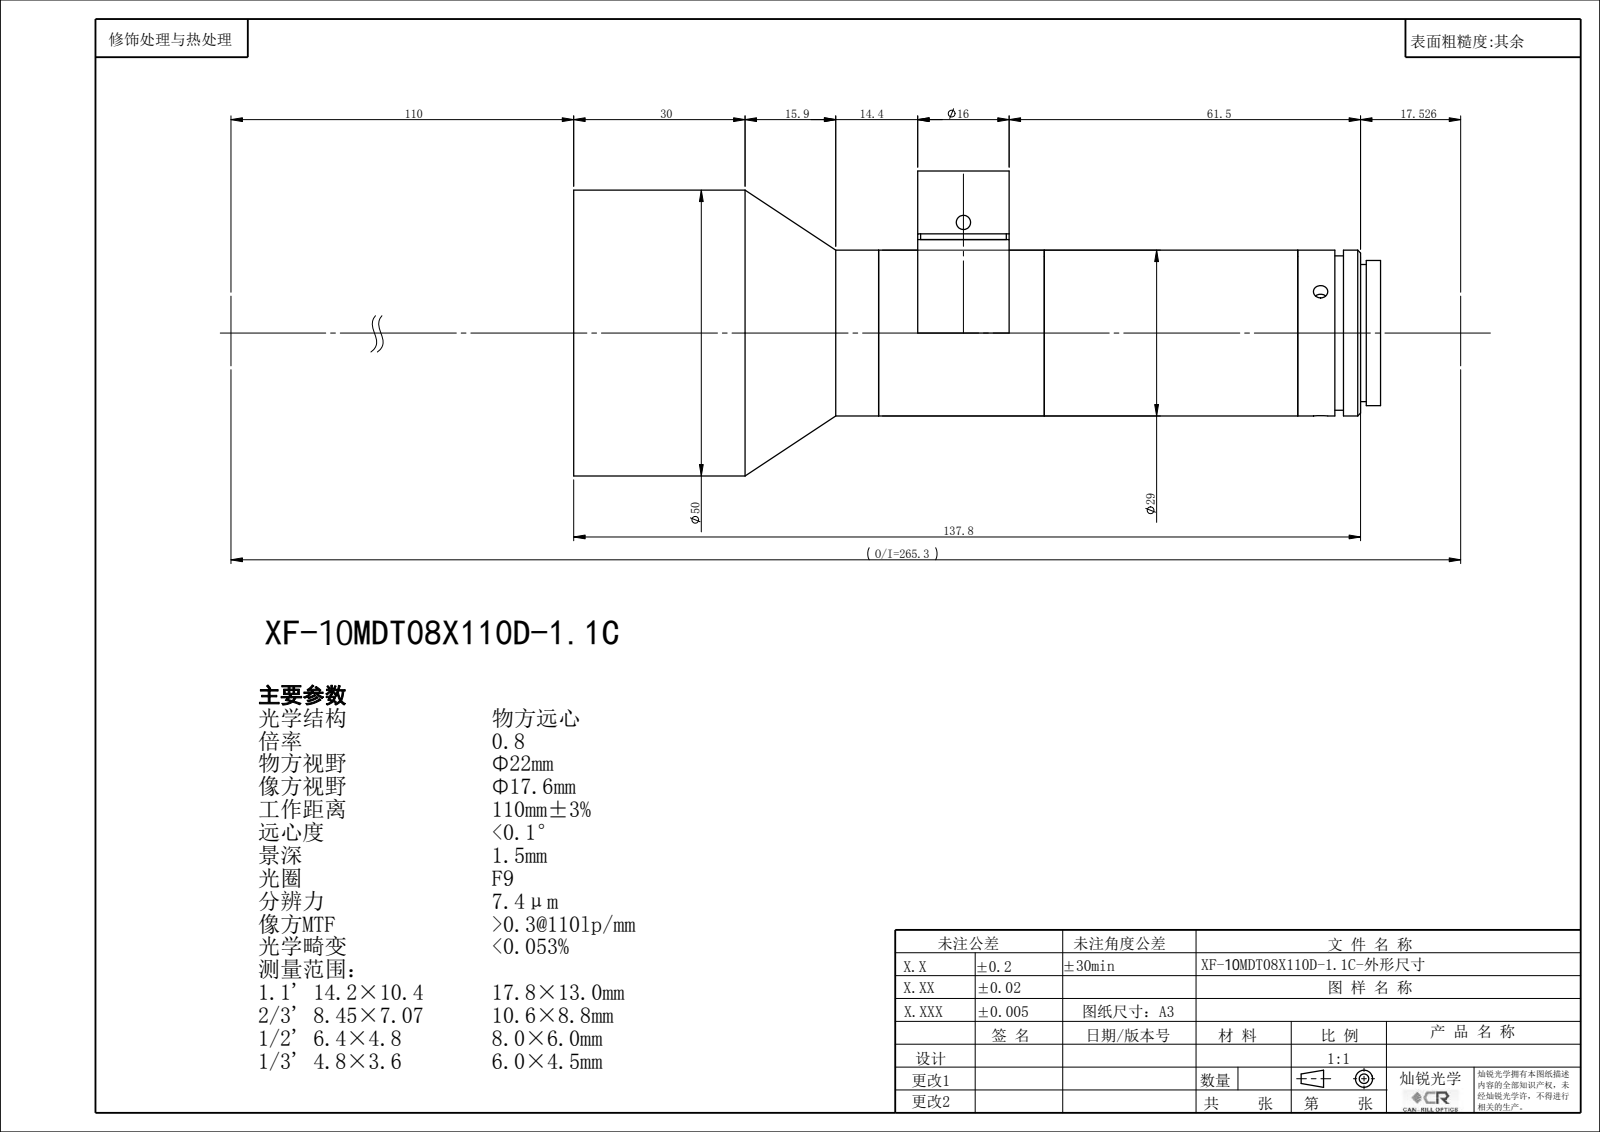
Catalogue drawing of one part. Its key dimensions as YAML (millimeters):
part_name: "XF-5MDT08X110D-1.1C"
step_written_by: "SolidWorks 2014 (CONFIG_CONTROL_DESIGN)"
units: millimeters
bodies: {solids: 0, faces: 97, planar: 36, cylindrical: 53, other: 8}
overall_size: [141.25, 53.35, 50]
round_holes:
  - {diameter: 2.2, count: 4}
  - {diameter: 2.5, count: 4}
  - {diameter: 1.6, count: 2}
  - {diameter: 8, count: 1}
  - {diameter: 14, count: 1}
  - {diameter: 17, count: 1}
  - {diameter: 21.4, count: 1}
  - {diameter: 42, count: 1}
  - {diameter: 46, count: 1}
round_bosses_or_shafts:
  - {diameter: 50, count: 1}
  - {diameter: 29, count: 1}
  - {diameter: 27, count: 1}
  - {diameter: 25.4, count: 1}
  - {diameter: 24, count: 1}
  - {diameter: 16, count: 1}
face_to_face_distances: [1, 29, 126.75, 4.17, 122.58, 11, 5.5, 135.75, 131.58, 9]
hole_center_spacings: [11.66, 12, 20, 23.32, 57.4, 69.25, 62.52]
